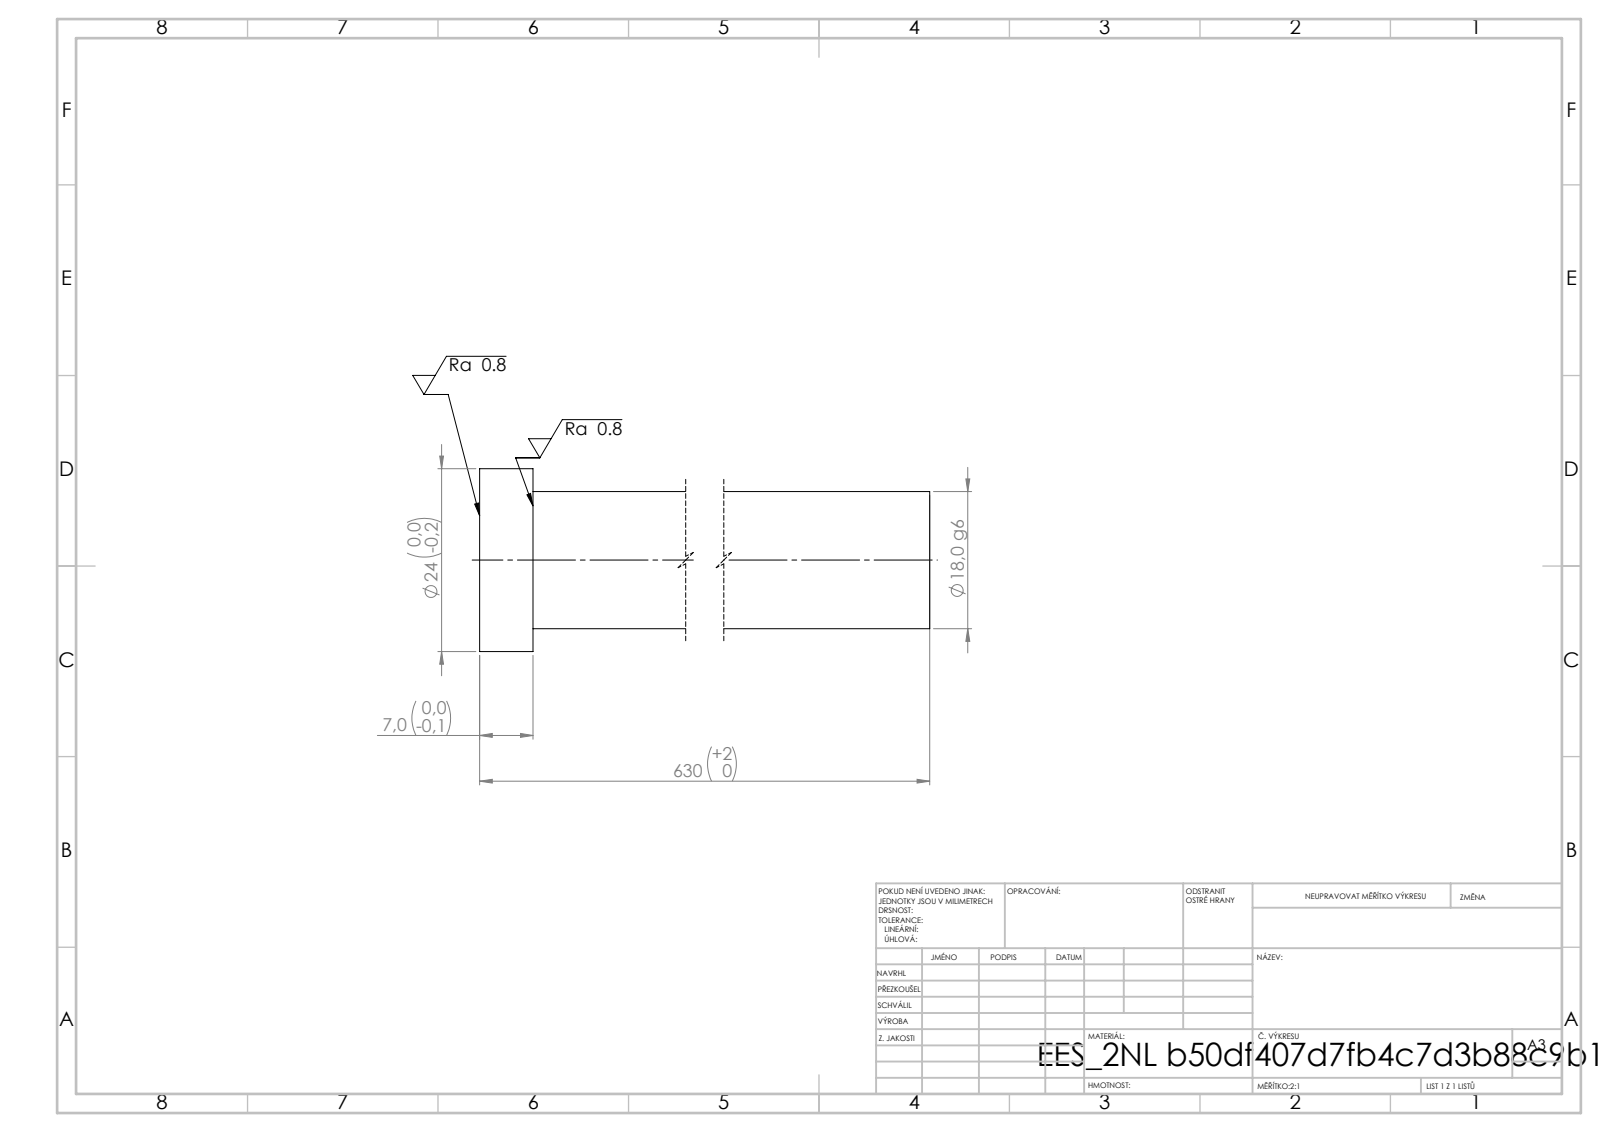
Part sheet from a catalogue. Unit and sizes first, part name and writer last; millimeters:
Units: millimetres
Overall size (bounding box): 630 × 24 × 24
Round bosses / shafts (diameter × count): ⌀24 ×1, ⌀18 ×1
Main face-to-face distances: 630, 7, 623
Volume: 161 701 mm³ · Surface area: 36 662 mm²
Bodies: 1 solid, 7 faces (3 planar, 4 cylindrical, 0 other)
STEP written by: SolidWorks 2019 (CONFIG_CONTROL_DESIGN)
